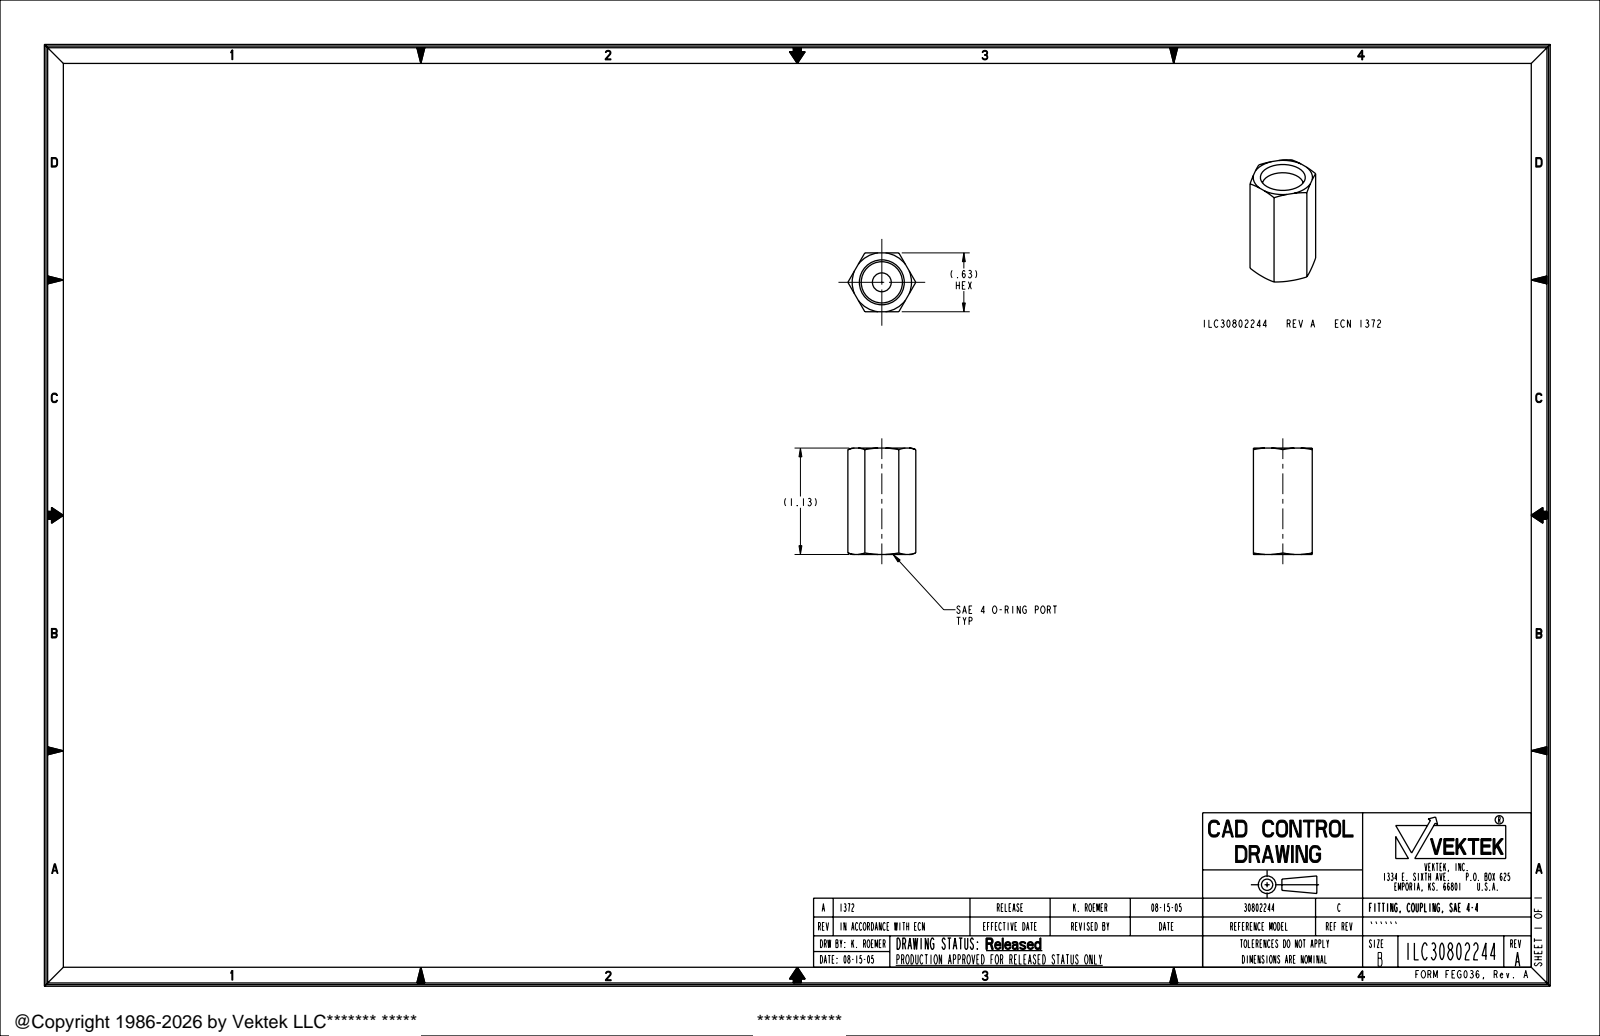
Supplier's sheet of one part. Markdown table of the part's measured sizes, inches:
| quantity | value |
| --- | --- |
| part name | ILC30802244 |
| STEP written by | PRO/ENGINEER BY PARAMETRIC TECHNOLOGY CORPORATION, 2004290 (AUTOMOTIVE_DESIGN_CC2) |
| units | inches |
| bodies | 1 solid, 32 faces (10 planar, 6 cylindrical, 16 other) |
| overall size | 1.13 × 0.722 × 0.625 |
| volume | 0.222 in³ |
| surface area | 4.478 in² |
| round holes (diameter × count) | 0.2 × 1, 0.437 × 1 |
| main face-to-face distances | 0.625, 1.13, 0.547, 0.65, 0.103, 0.583, 0.48 |
